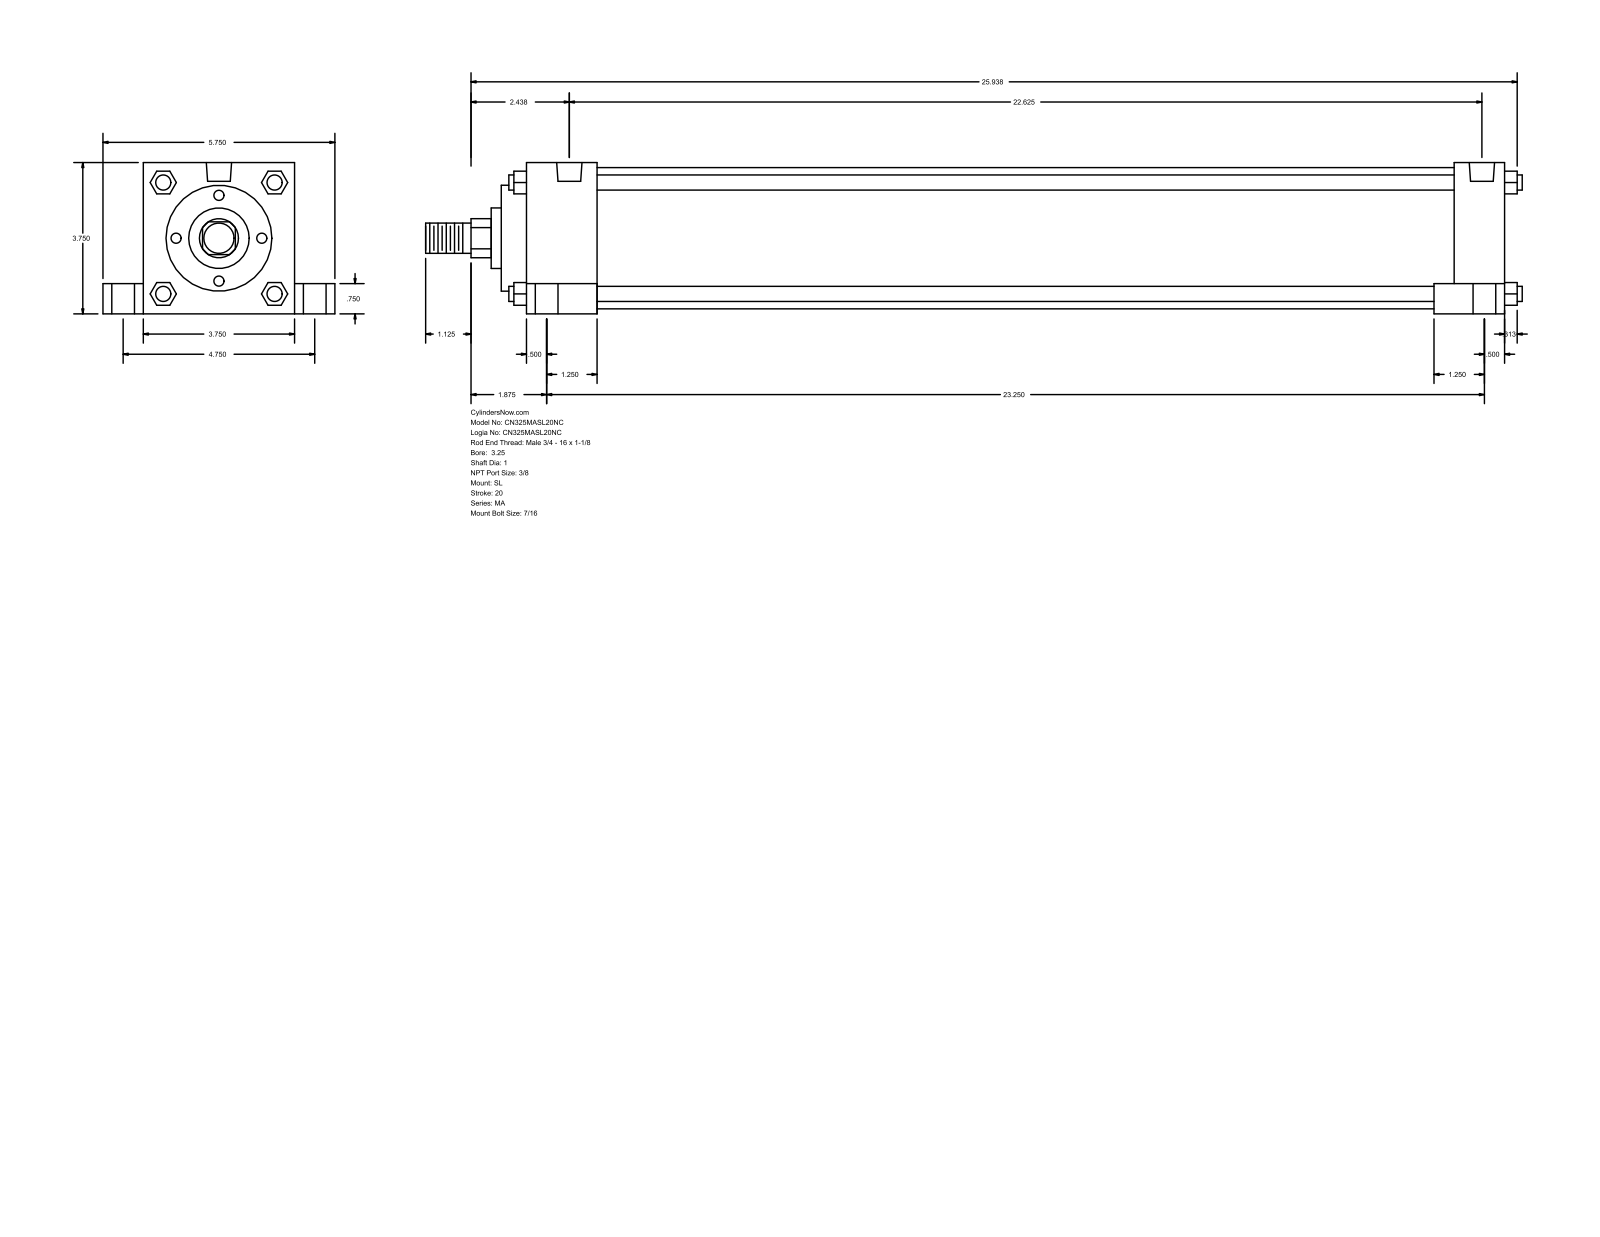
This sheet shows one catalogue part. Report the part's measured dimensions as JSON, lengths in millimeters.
{"part_name": "MA_SL__0325_1", "step_written_by": "GSSL Pune (CONFIG_CONTROL_DESIGN)", "units": "millimeters", "bodies": {"solids": 0, "faces": 150, "planar": 113, "cylindrical": 37, "other": 0}, "overall_size": [690.56, 146.05, 95.25], "round_holes": [[11.11, 4], [14.29, 4], [20.64, 4], [15.93, 2]], "round_bosses_or_shafts": [[9.53, 4], [88.9, 1], [66.67, 1], [38.1, 1], [25.4, 1], [19.05, 1]], "partial_cylinders_radius": [[12.29, 1]], "face_to_face_distances": [95.24, 615.96, 15.87, 25.41, 120.65, 19.05, 584.2, 31.76, 44.46, 539.74], "hole_center_spacings": [574.68, 4.76, 60.35, 60.66, 62, 63.27, 120.66, 565.16]}
